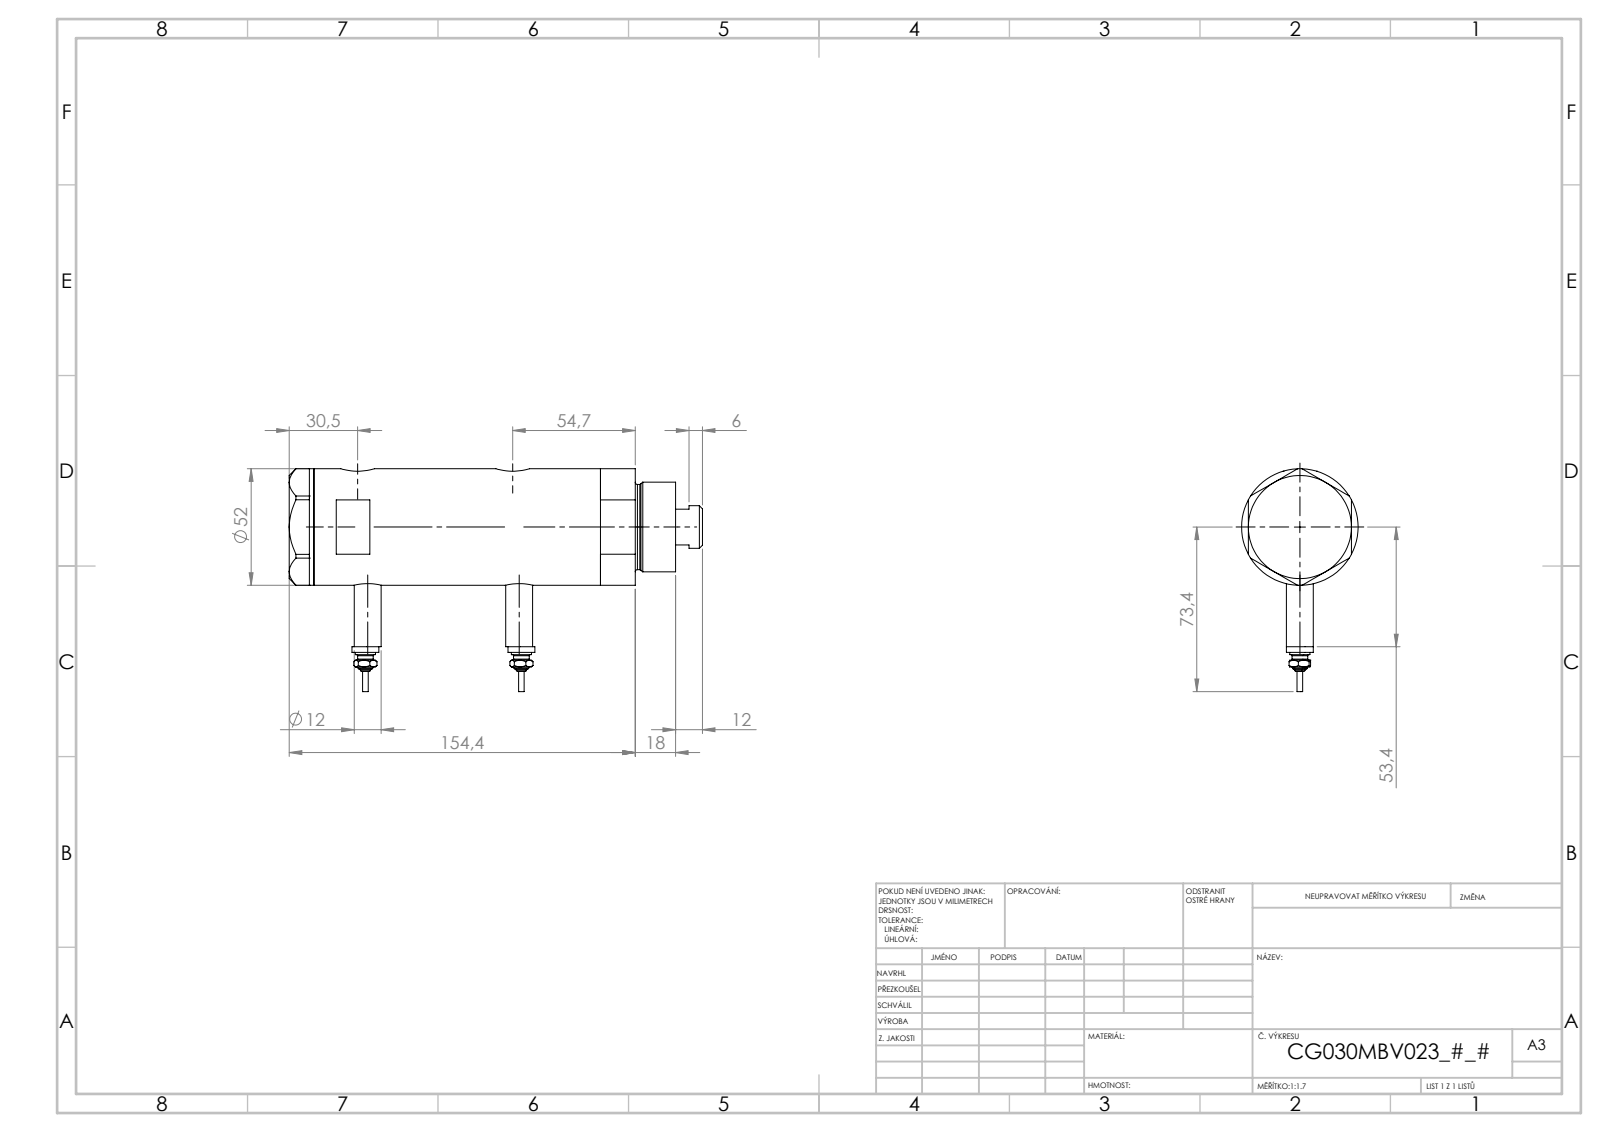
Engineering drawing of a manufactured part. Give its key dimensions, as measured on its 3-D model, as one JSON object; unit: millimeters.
{"part_name": "V270CG_MIDDLE; V270CG_BACK; V270CG_FRONT; Switch (+1 more)", "step_written_by": "SolidWorks 2019 (CONFIG_CONTROL_DESIGN)", "units": "millimeters", "bodies": {"solids": 6, "faces": 226, "planar": 93, "cylindrical": 69, "other": 64}, "overall_size": [184.4, 99.4, 52], "volume_mm3": 343683, "surface_area_mm2": 80133, "round_holes": [[9.73, 2], [12.5, 2], [15, 2], [6.5, 1], [20, 1], [21.5, 1], [30, 1], [33, 1], [44, 1]], "round_bosses_or_shafts": [[12, 4], [9, 2], [7, 2], [4.5, 2], [2.5, 2], [52, 1], [40, 1], [38, 1]], "face_to_face_distances": [91.5, 23.8, 67.7, 11, 34.8, 102.5, 46, 36.4, 138.9, 127.9], "hole_center_spacings": [2.9, 4.5, 64.7, 67.6, 69.2, 72.1]}
